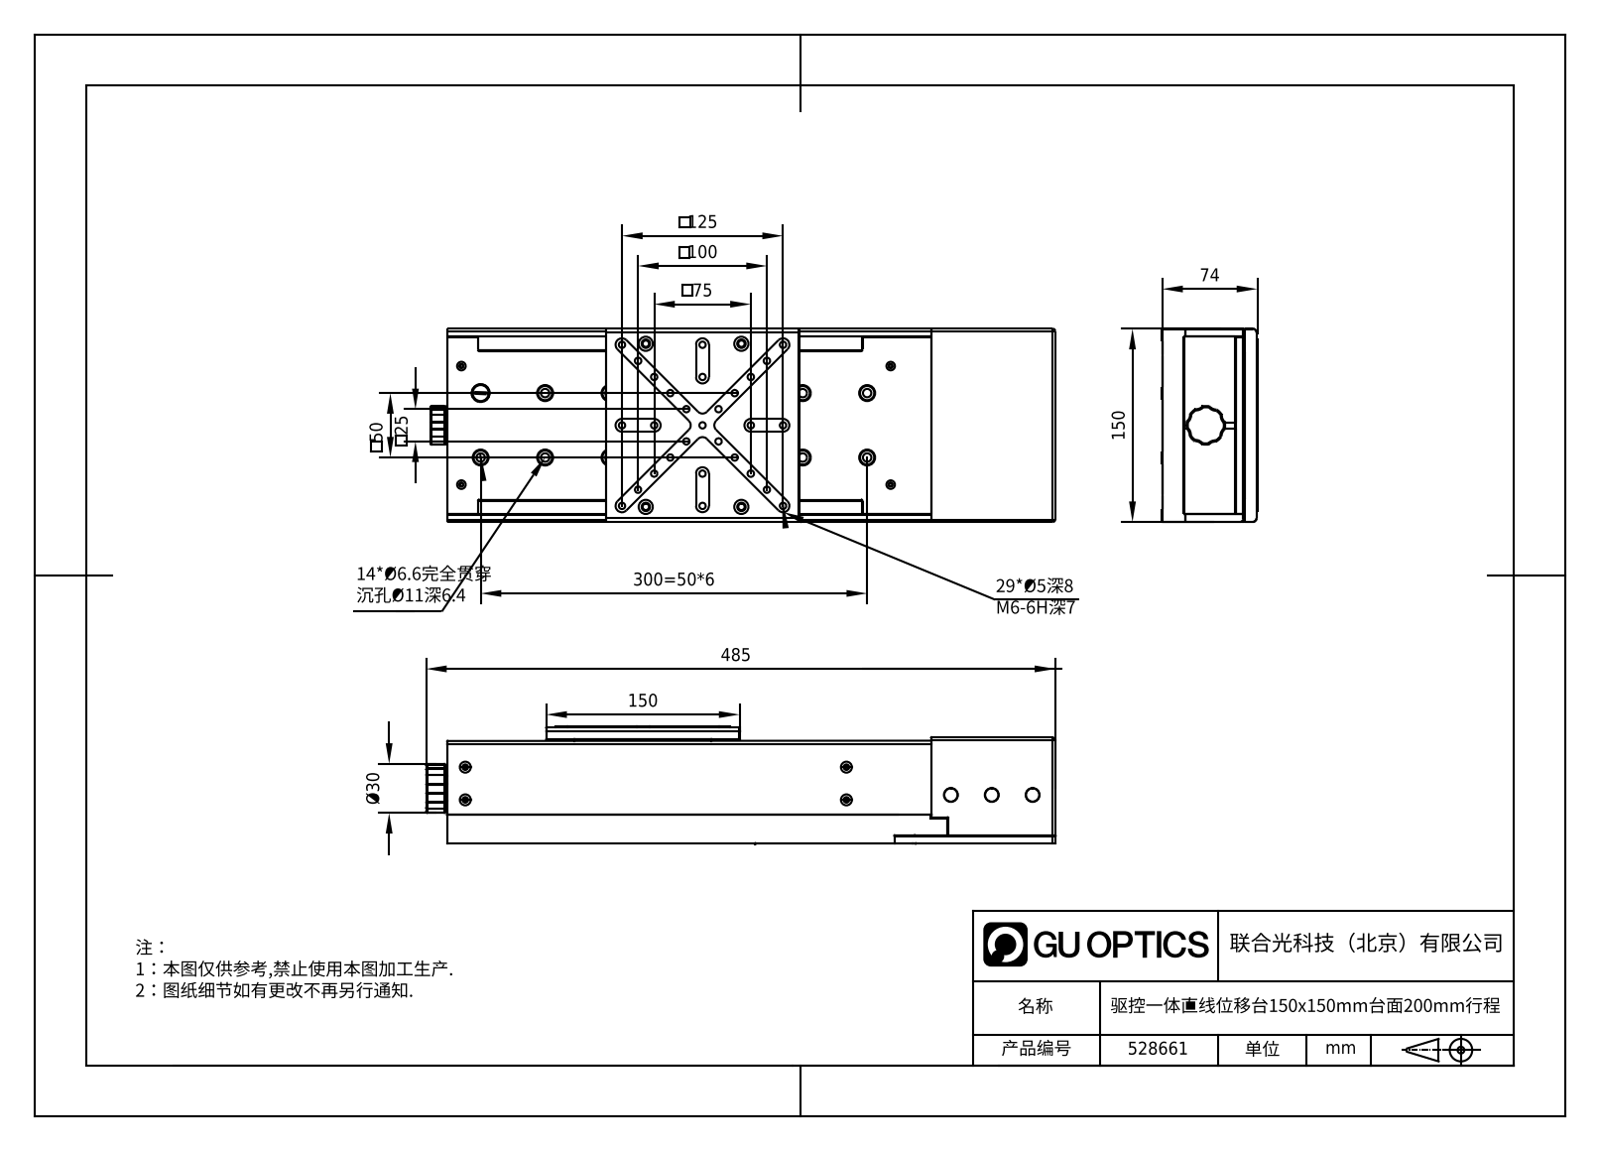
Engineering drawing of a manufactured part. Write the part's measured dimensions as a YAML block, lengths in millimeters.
part_name: "528661"
step_written_by: "SolidWorks 2020 (CONFIG_CONTROL_DESIGN)"
units: millimeters
bodies: {solids: 45, faces: 2635, planar: 1410, cylindrical: 776, other: 449}
overall_size: [485, 150, 74]
volume: 3057000
surface_area: 689586
round_holes:
  - {diameter: 5, count: 40}
  - {diameter: 3.4, count: 27}
  - {diameter: 6.6, count: 20}
  - {diameter: 11, count: 20}
  - {diameter: 6.5, count: 19}
  - {diameter: 3.5, count: 16}
  - {diameter: 2.5, count: 15}
  - {diameter: 12.5, count: 14}
  - {diameter: 6, count: 12}
  - {diameter: 3.3, count: 9}
  - {diameter: 2.46, count: 8}
  - {diameter: 2.46, count: 8}
round_bosses_or_shafts:
  - {diameter: 38.2, count: 1}
  - {diameter: 24, count: 1}
  - {diameter: 19, count: 1}
  - {diameter: 16, count: 1}
  - {diameter: 14, count: 1}
  - {diameter: 10.56, count: 1}
  - {diameter: 3, count: 1}
partial_cylinders:
  - {radius: 1, count: 20}
  - {radius: 5, count: 16}
  - {radius: 2, count: 13}
  - {radius: 7.5, count: 8}
  - {radius: 4, count: 5}
  - {radius: 1.5, count: 4}
  - {radius: 0.3, count: 2}
  - {radius: 0.75, count: 2}
face_to_face_distances: [6, 39, 1, 57, 18, 63, 45, 144, 17, 9]
hole_center_spacings: [50, 70.71, 100, 111.8, 150, 158.11, 200, 40]
